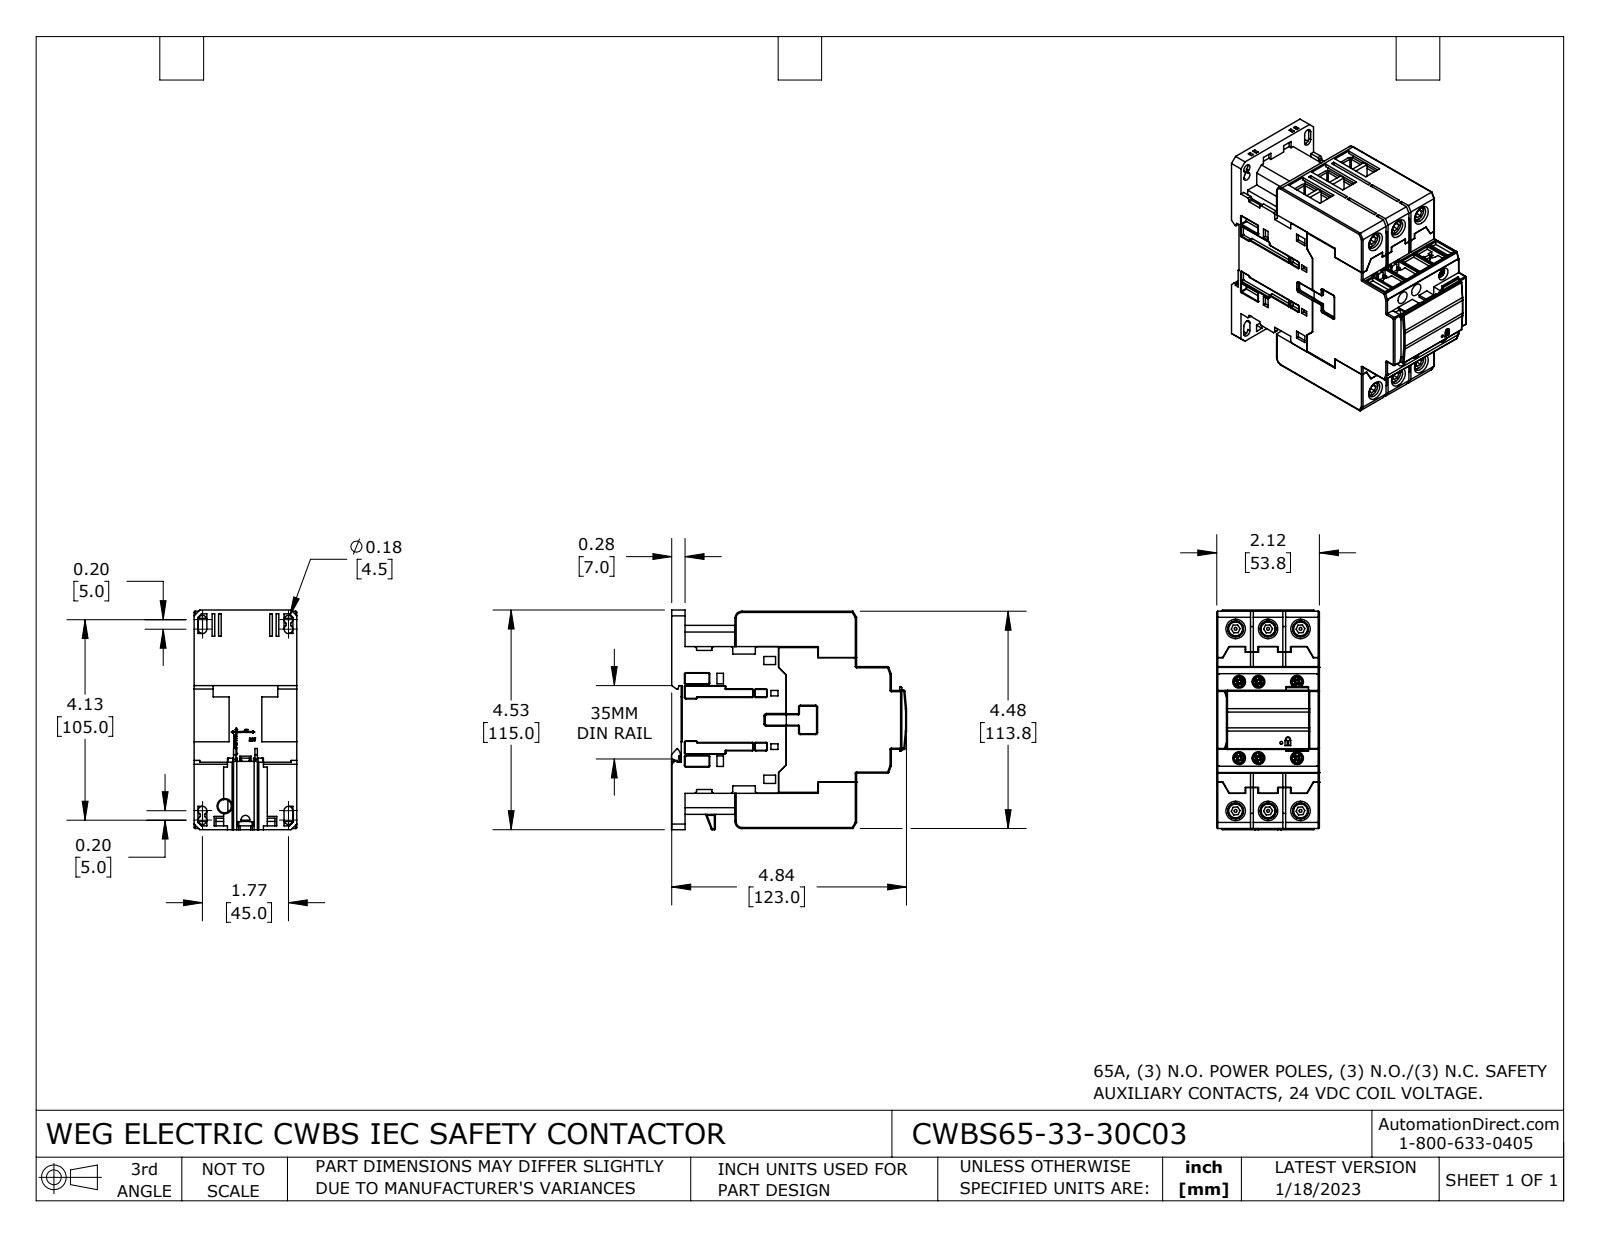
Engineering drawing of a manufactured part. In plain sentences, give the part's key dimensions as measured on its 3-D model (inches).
The part is named "CWBS65-33-30C03". Its 3-D file was written by "SolidWorks 2021 (CONFIG_CONTROL_DESIGN)". It is 37 solids with 2637 faces: 1669 planar, 550 cylindrical and 418 other. Overall it measures 4.846 by 4.528 by 2.118 inches. Its volume is 33.67 cubic inches and its surface area 209.3 square inches. Round holes: 6 of diameter 0.124, 6 of diameter 0.197, 6 of diameter 0.264, 6 of diameter 0.323, 4 of diameter 0.177, 2 of diameter 0.125, 2 of diameter 0.276, 1 of diameter 0.059. Round bosses or shafts: 6 of diameter 0.343, 6 of diameter 0.236, 6 of diameter 0.135. Partial cylindrical surfaces (rounded edges, fillets, slot ends): 89 of radius 0.02, 69 of radius 0.012, 48 of radius 0.004, 42 of radius 0.024, 18 of radius 0.079, 5 of radius 0.089, 3 of radius 0.039, 3 of radius 0.059. The main face-to-face distances are 0.059, 2.118, 0.669, 0.728, 3.024, 3.752, 0.108, 0.217, 3.811, 0.098. The hole center spacings are 0.669, 1.091, 1.241, 1.669, 2.665, 2.73, 2.949, 3.811.
